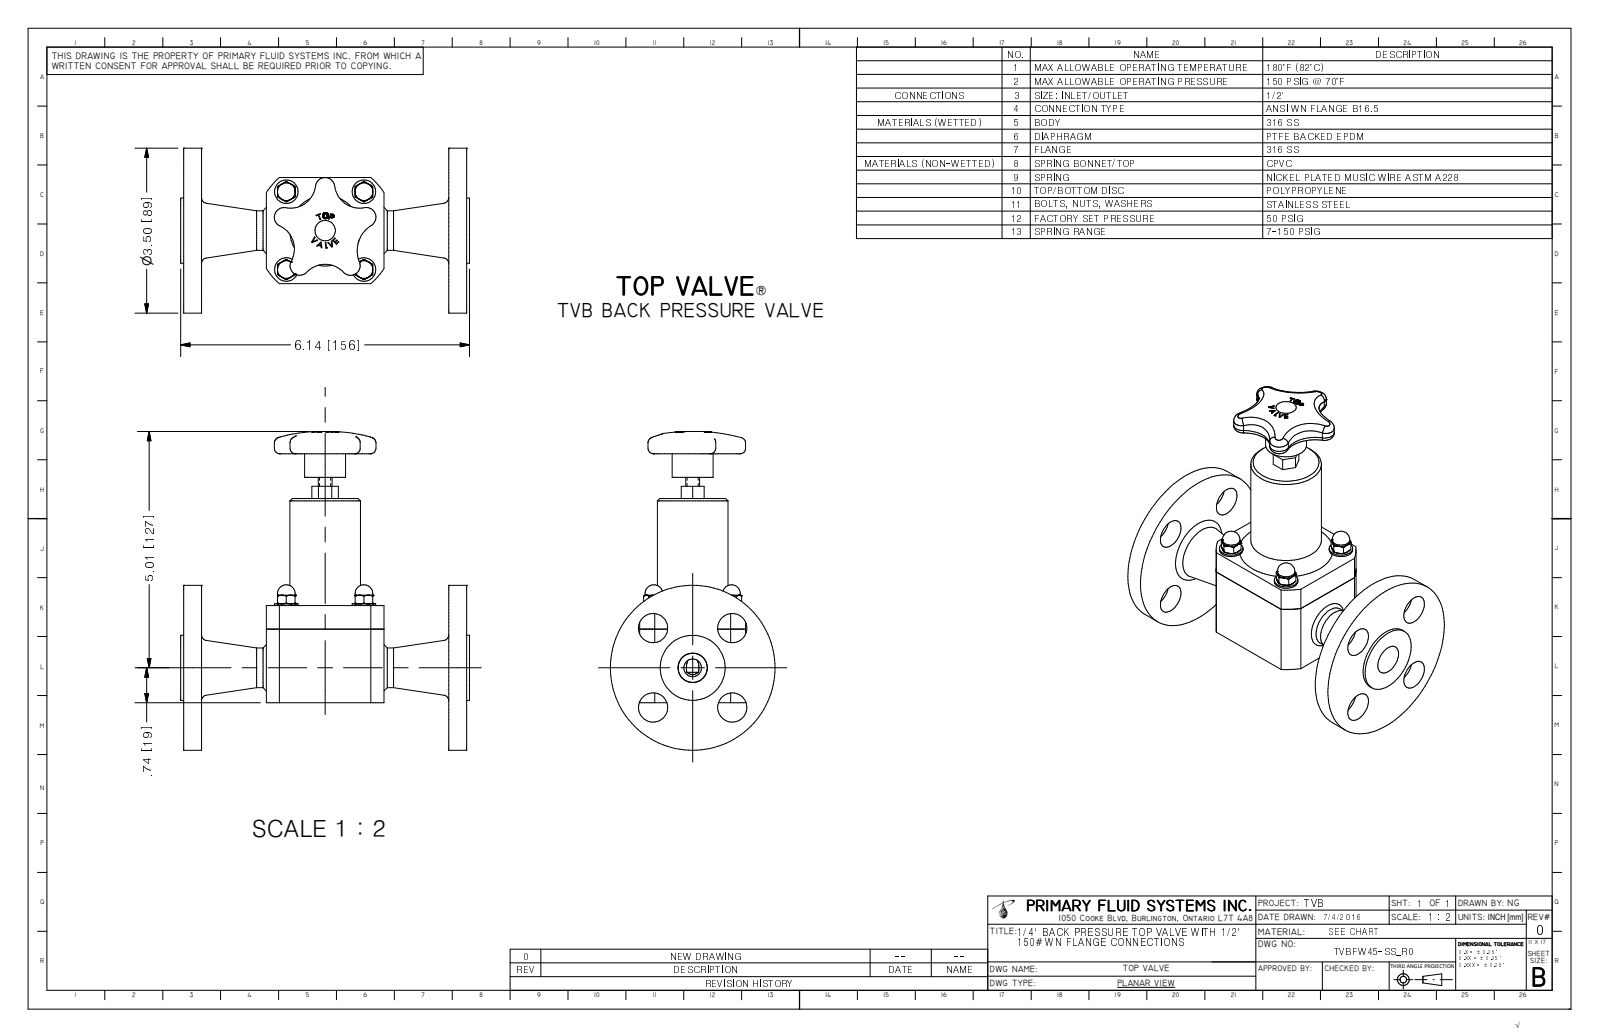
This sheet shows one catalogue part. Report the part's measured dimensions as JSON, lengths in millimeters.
{"part_name": "TVBFW45-SS-R0", "step_written_by": "Autodesk Inventor 2009 (AUTOMOTIVE_DESIGN)", "units": "millimeters", "bodies": {"solids": 1, "faces": 373, "planar": 150, "cylindrical": 63, "other": 160}, "overall_size": [171.8, 156, 88.9], "volume_mm3": 398500, "surface_area_mm2": 74130, "round_holes": [[3.7, 4], [15.7, 4], [15.8, 1]], "round_bosses_or_shafts": [[12.7, 4], [9.5, 4], [7.9, 4], [4.8, 4], [88.9, 1], [38.1, 1], [35.1, 1], [22.1, 1]], "partial_cylinders_radius": [[2.2, 5], [5.2, 5], [13.6, 4], [16.7, 4], [15.9, 1], [18.9, 1], [37.8, 1]], "face_to_face_distances": [9.7, 143.1, 152.8, 133.5, 44.6, 108.1, 35, 98.5, 57.2, 63.5], "hole_center_spacings": [30.2, 30.2, 41.9, 41.9, 42.7, 42.7, 59.3, 60.5]}
